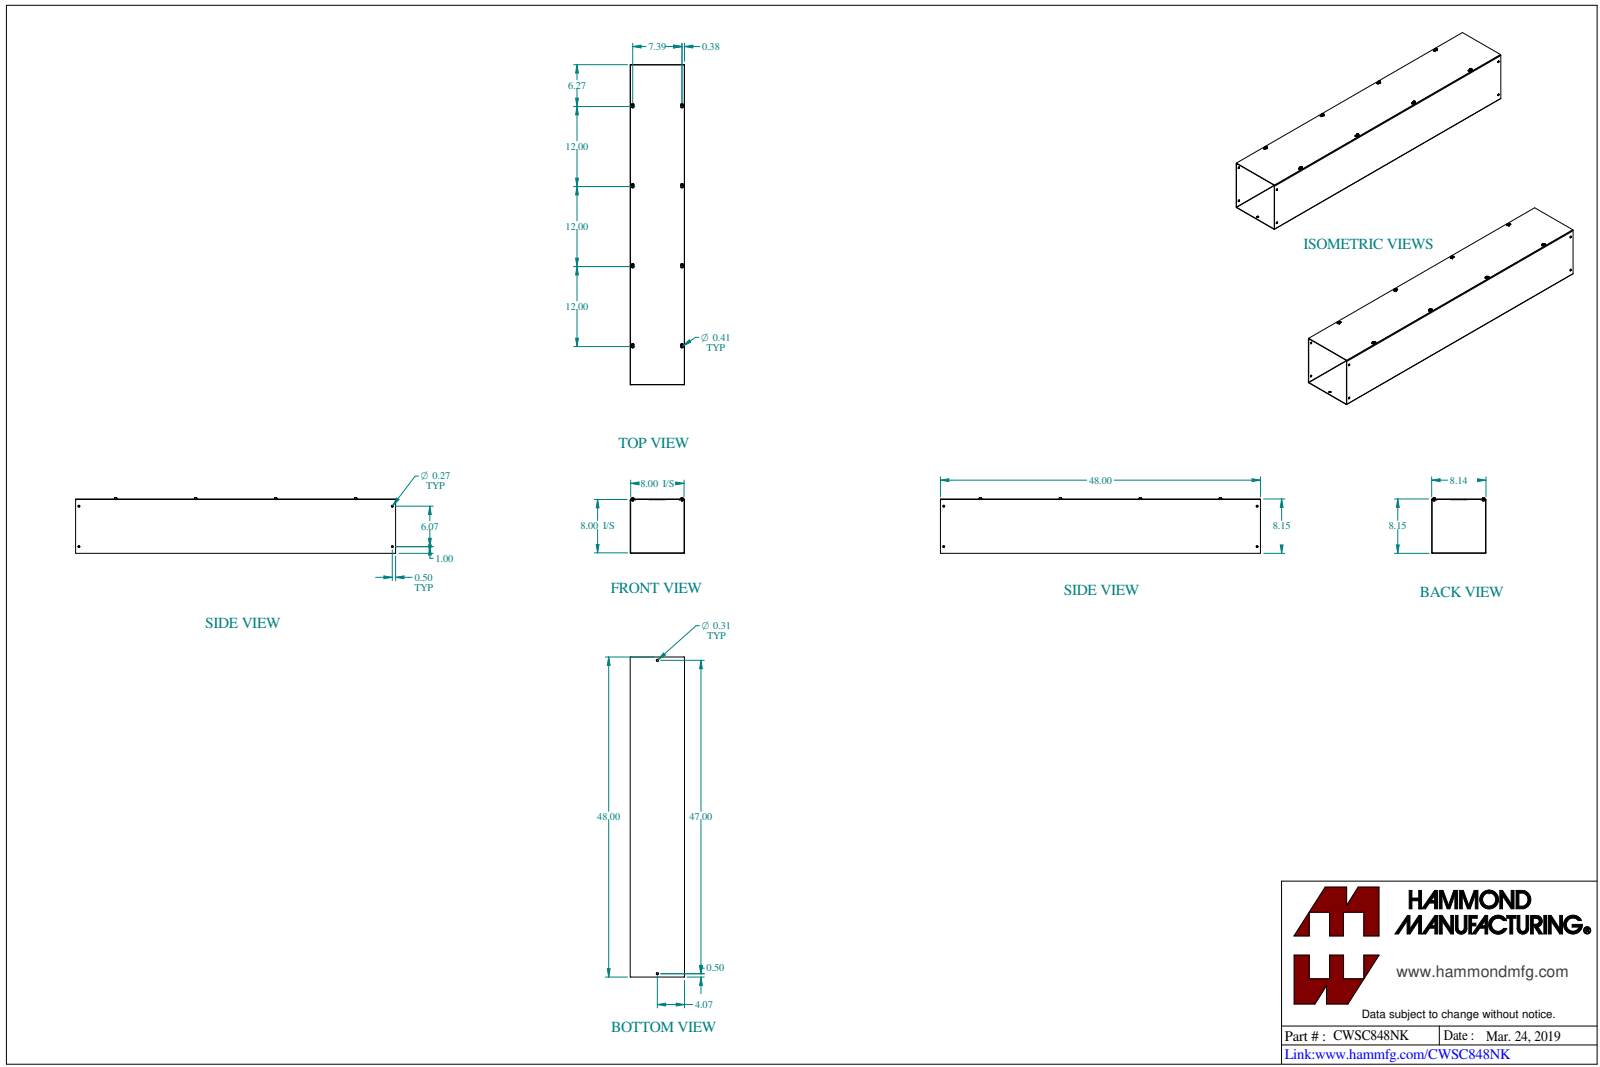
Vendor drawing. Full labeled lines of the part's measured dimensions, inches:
Part name (STEP PRODUCT): CWSC848NK
STEP written by: SolidWorks 2023 (CONFIG_CONTROL_DESIGN)
Units: inches
Bodies: 10 solids, 304 faces (148 planar, 108 cylindrical, 48 other)
Overall size (bounding box): 48 × 8.325 × 8.144
Volume: 117.8 in³ · Surface area: 3 228 in²
Round holes (diameter × count): ⌀0.177 ×8, ⌀0.266 ×4, ⌀0.313 ×2
Round bosses / shafts (diameter × count): ⌀0.375 ×8, ⌀0.19 ×8
Partial cylindrical surfaces — rounded edges, fillets, slot ends (radius × count): R0.125 ×8, R0.203 ×8, R0.036 ×4, R0.108 ×4
Main face-to-face distances: 0.072, 8.072, 8, 0.078, 8.15, 8.078, 8.144, 7.928, 0.15, 0.031
Hole centre spacings: 12, 14.095, 6.627, 7.394, 17.886, 24, 25.113, 29.731
